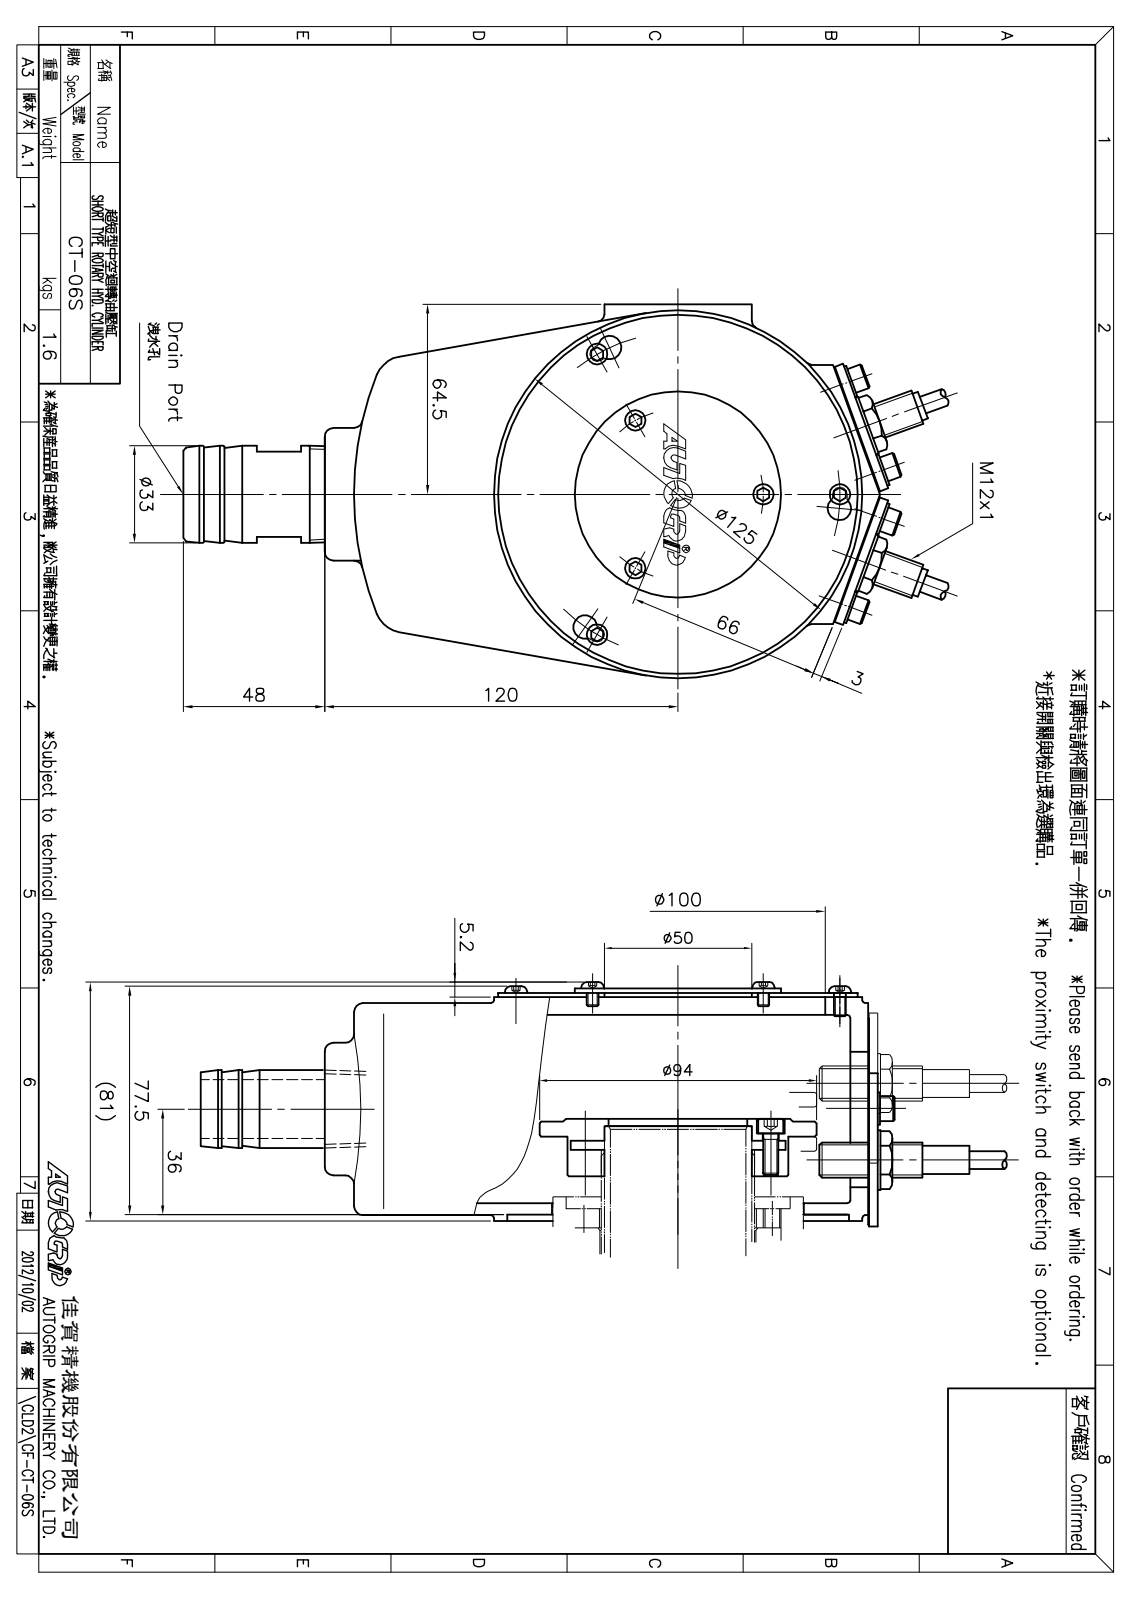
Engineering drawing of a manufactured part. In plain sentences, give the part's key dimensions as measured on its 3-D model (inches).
The part is named "CF-CT-06-11000; CF-CT-06S; CF-CT-06-12000; CT-08洩油管 (+3 more)". Its 3-D file was written by "SolidWorks 2016 (CONFIG_CONTROL_DESIGN)". It is 23 solids with 469 faces: 273 planar, 122 cylindrical and 74 other. Overall it measures 9.567 by 5 by 3.189 inches. Its volume is 22.18 cubic inches and its surface area 304.5 square inches. Round holes: 6 of diameter 0.13, 6 of diameter 0.165, 6 of diameter 0.217, 3 of diameter 0.177, 2 of diameter 0.354, 2 of diameter 0.472, 1 of diameter 0.984, 1 of diameter 1.85, 1 of diameter 1.969, 1 of diameter 2.913, 1 of diameter 3.366, 1 of diameter 3.937. Round bosses or shafts: 6 of diameter 0.276, 6 of diameter 0.157, 4 of diameter 0.433, 4 of diameter 0.335, 4 of diameter 0.197, 1 of diameter 4.921, 1 of diameter 4.803, 1 of diameter 3.701. Partial cylindrical surfaces (rounded edges, fillets, slot ends): 16 of radius 0.108, 10 of radius 0.118, 8 of radius 0.276, 6 of radius 0.079, 5 of radius 0.098, 3 of radius 0.157, 2 of radius 0.236, 2 of radius 0.394. The main face-to-face distances are 0.059, 0.157, 0.236, 0.079, 2.756, 2.677, 2.815, 0.118, 2.913, 0.295. The hole center spacings are 2.909, 1.024, 1.142, 2.165, 3.75, 0.824, 0.824, 1.24.
